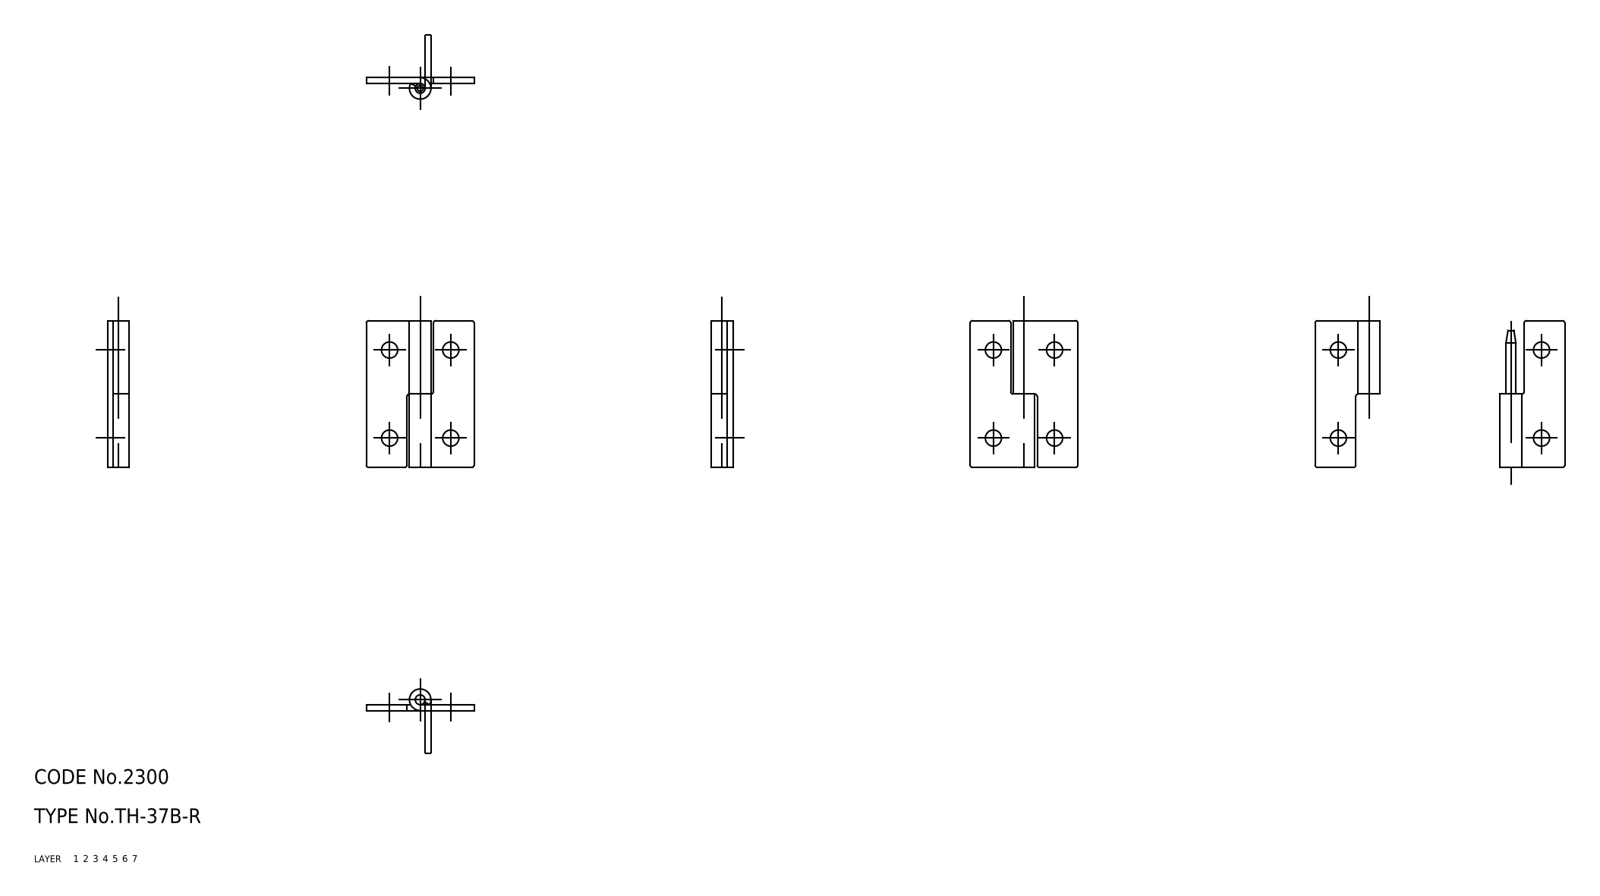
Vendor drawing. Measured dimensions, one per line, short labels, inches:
name: shaft; hinge piece_B; hinge piece_A; TH_37B_R_8291_36
written by: CADfix (AUTOMOTIVE_DESIGN)
unit: in
bodies: 3 solids, 42 faces (0 planar, 0 cylindrical, 42 other)
size: 1.181 × 0.866 × 0.173
volume: 0.063 in³; area: 3.171 in²
